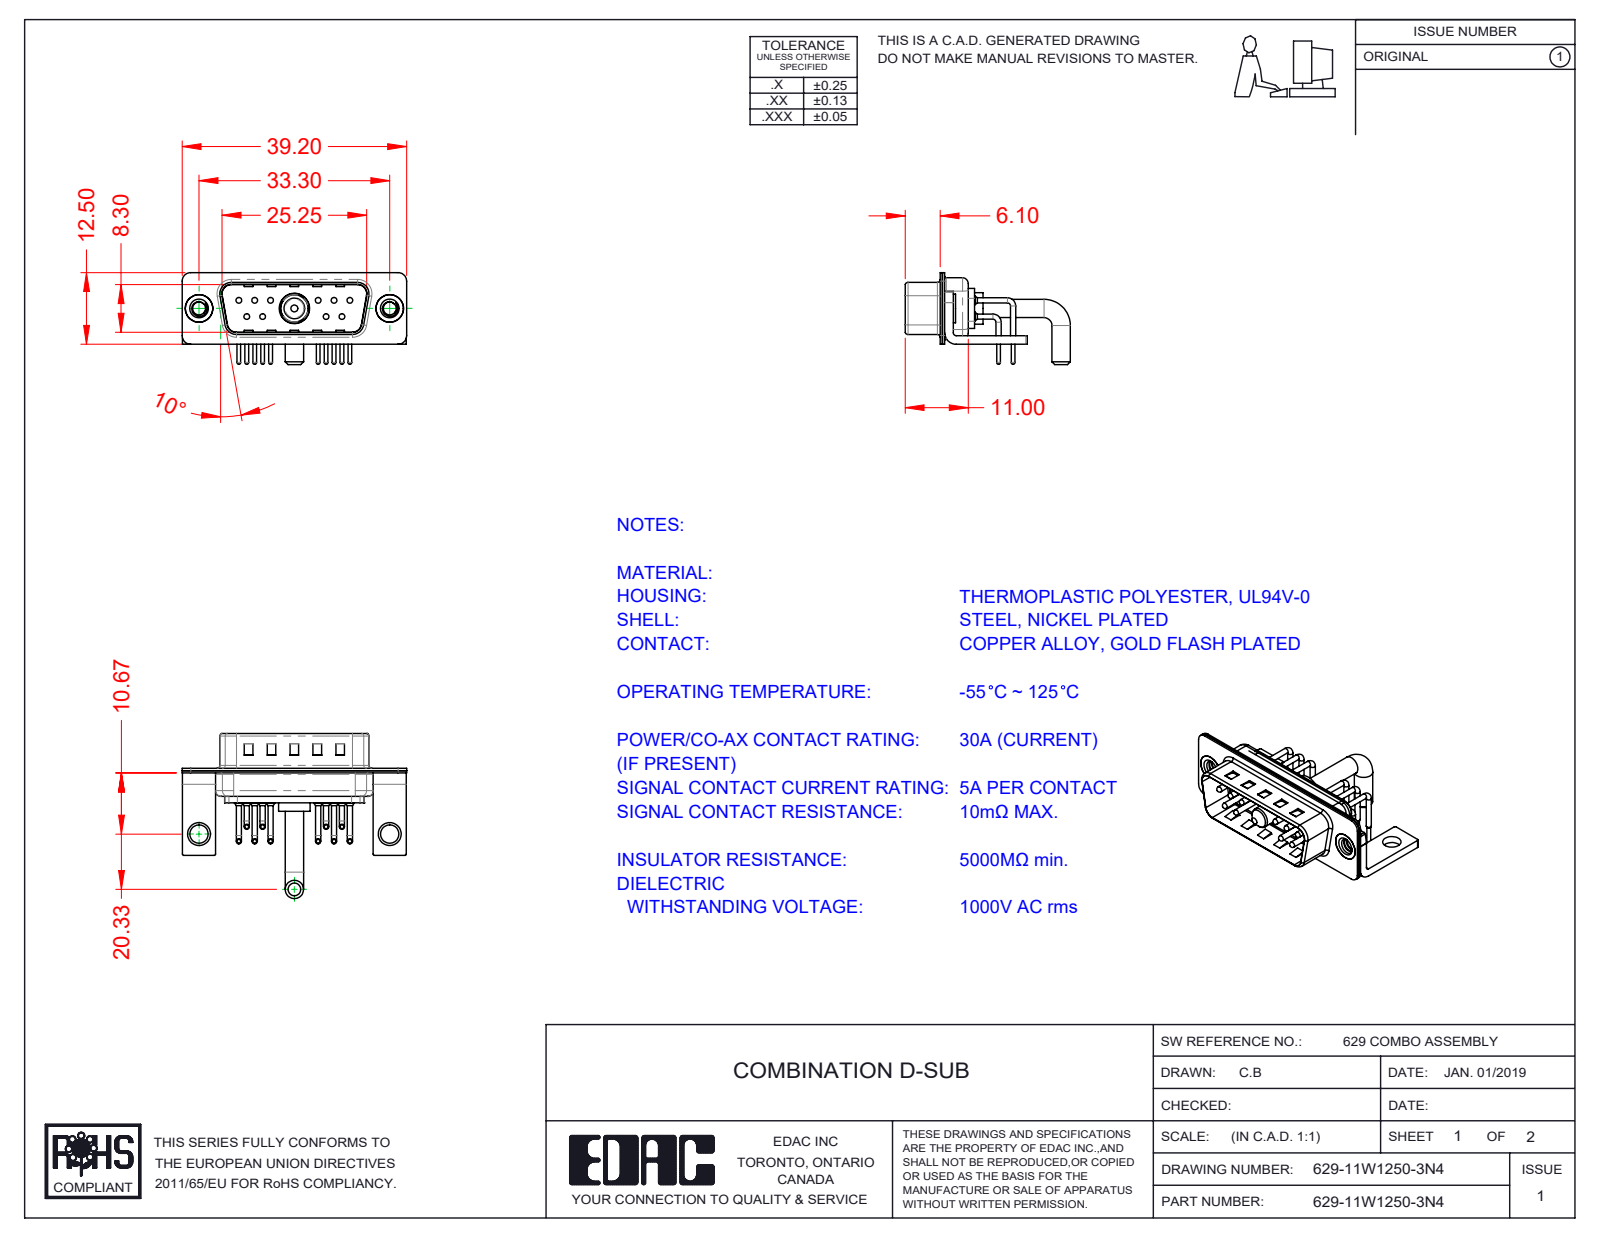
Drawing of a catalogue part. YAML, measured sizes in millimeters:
part_name: "629Combo Housing_11W1; 629Combo Threaded Rivet_3; 629Combo Stabilizer Bracket; Power Pin_Ext 30A RA (+5 more)"
step_written_by: "SolidWorks 2020 (CONFIG_CONTROL_DESIGN)"
units: millimeters
bodies: {solids: 19, faces: 1536, planar: 818, cylindrical: 536, other: 182}
overall_size: [39.2, 28.83, 16.05]
volume: 2416
surface_area: 5910
round_holes:
  - {diameter: 0.75, count: 10}
  - {diameter: 1.6, count: 10}
  - {diameter: 2, count: 10}
  - {diameter: 2.26, count: 2}
  - {diameter: 3.2, count: 2}
  - {diameter: 4, count: 2}
  - {diameter: 4.8, count: 2}
  - {diameter: 4.85, count: 1}
  - {diameter: 5.3, count: 1}
round_bosses_or_shafts:
  - {diameter: 0.9, count: 20}
  - {diameter: 1.5, count: 10}
  - {diameter: 1, count: 10}
  - {diameter: 0.65, count: 10}
  - {diameter: 5, count: 2}
  - {diameter: 4.9, count: 2}
  - {diameter: 3.2, count: 2}
  - {diameter: 5.5, count: 1}
partial_cylinders:
  - {radius: 0.25, count: 16}
  - {radius: 1.5, count: 16}
  - {radius: 2, count: 13}
  - {radius: 1.01, count: 10}
  - {radius: 0.5, count: 9}
  - {radius: 1.6, count: 8}
  - {radius: 1, count: 7}
  - {radius: 0.6, count: 4}
face_to_face_distances: [0.4, 0.8, 1.5, 9.5, 9.1, 8.7, 9.9, 0.6, 1.9, 5.2]
hole_center_spacings: [3.16, 2.77, 13.85, 11.08, 16.62, 5.03, 5.04, 5.54]
